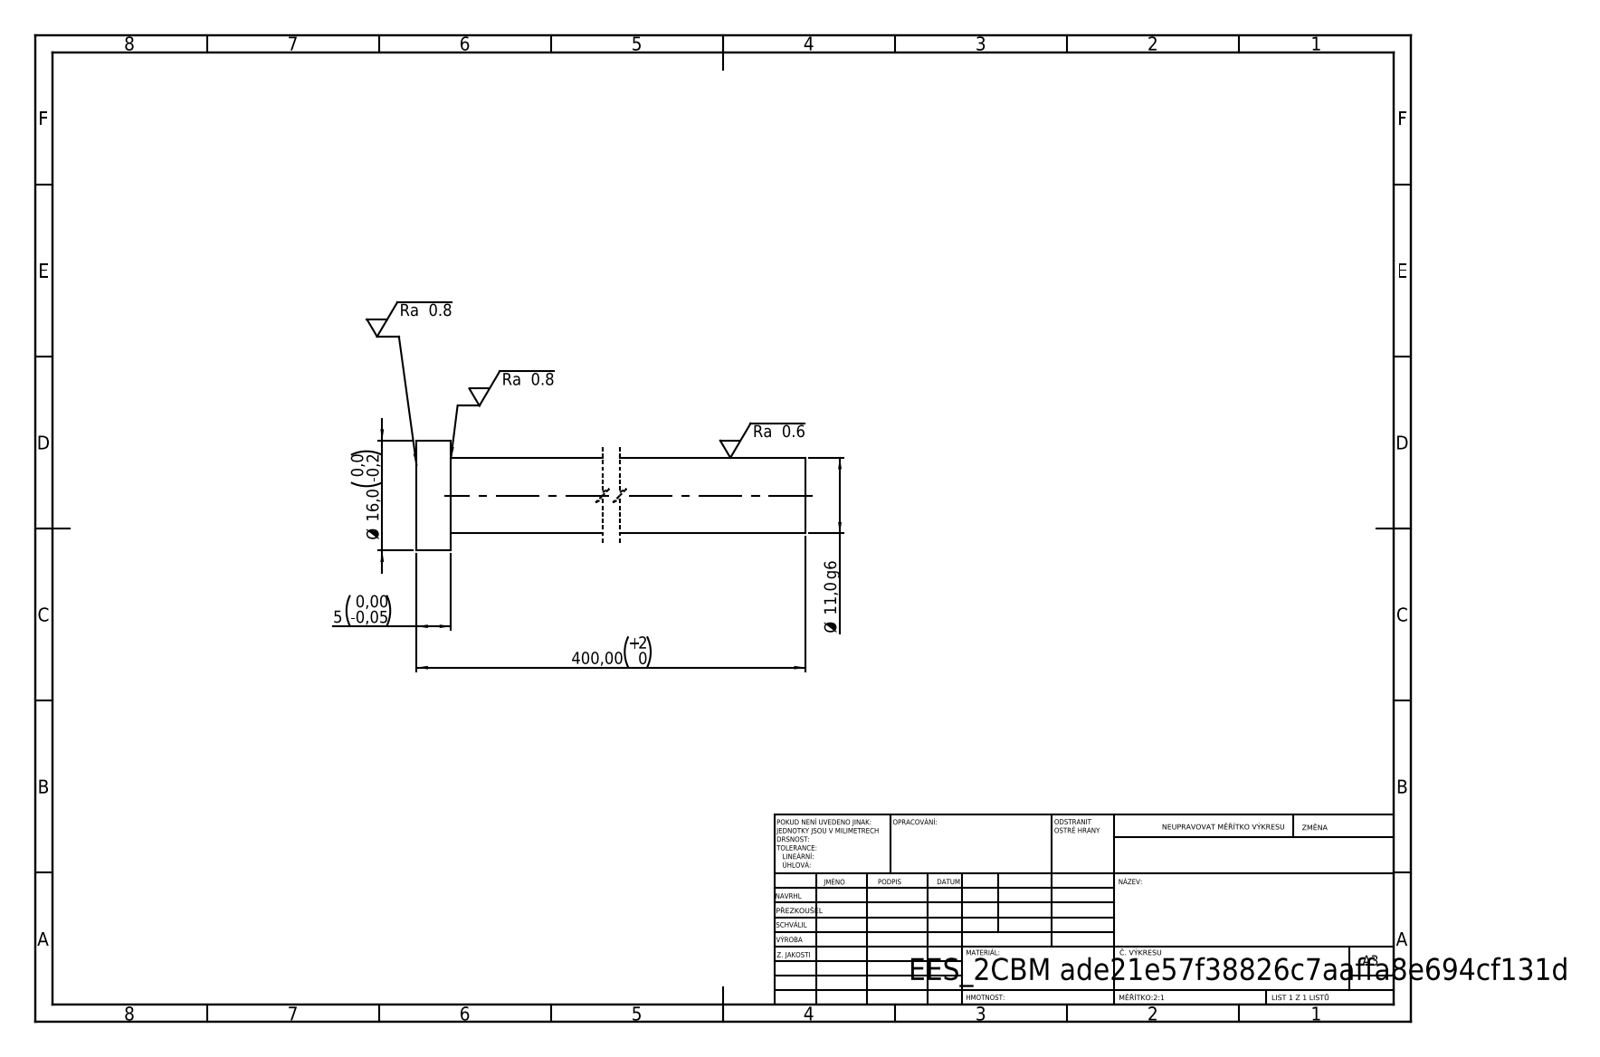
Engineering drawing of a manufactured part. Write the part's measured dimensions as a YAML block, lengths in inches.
step_written_by: "SolidWorks 2019 (CONFIG_CONTROL_DESIGN)"
units: inches
bodies: {solids: 1, faces: 7, planar: 3, cylindrical: 4, other: 0}
overall_size: [15.748, 0.63, 0.63]
volume: 2.352
surface_area: 22.17
round_bosses_or_shafts:
  - {diameter: 0.63, count: 1}
  - {diameter: 0.433, count: 1}
face_to_face_distances: [0.197, 15.748, 15.551]
